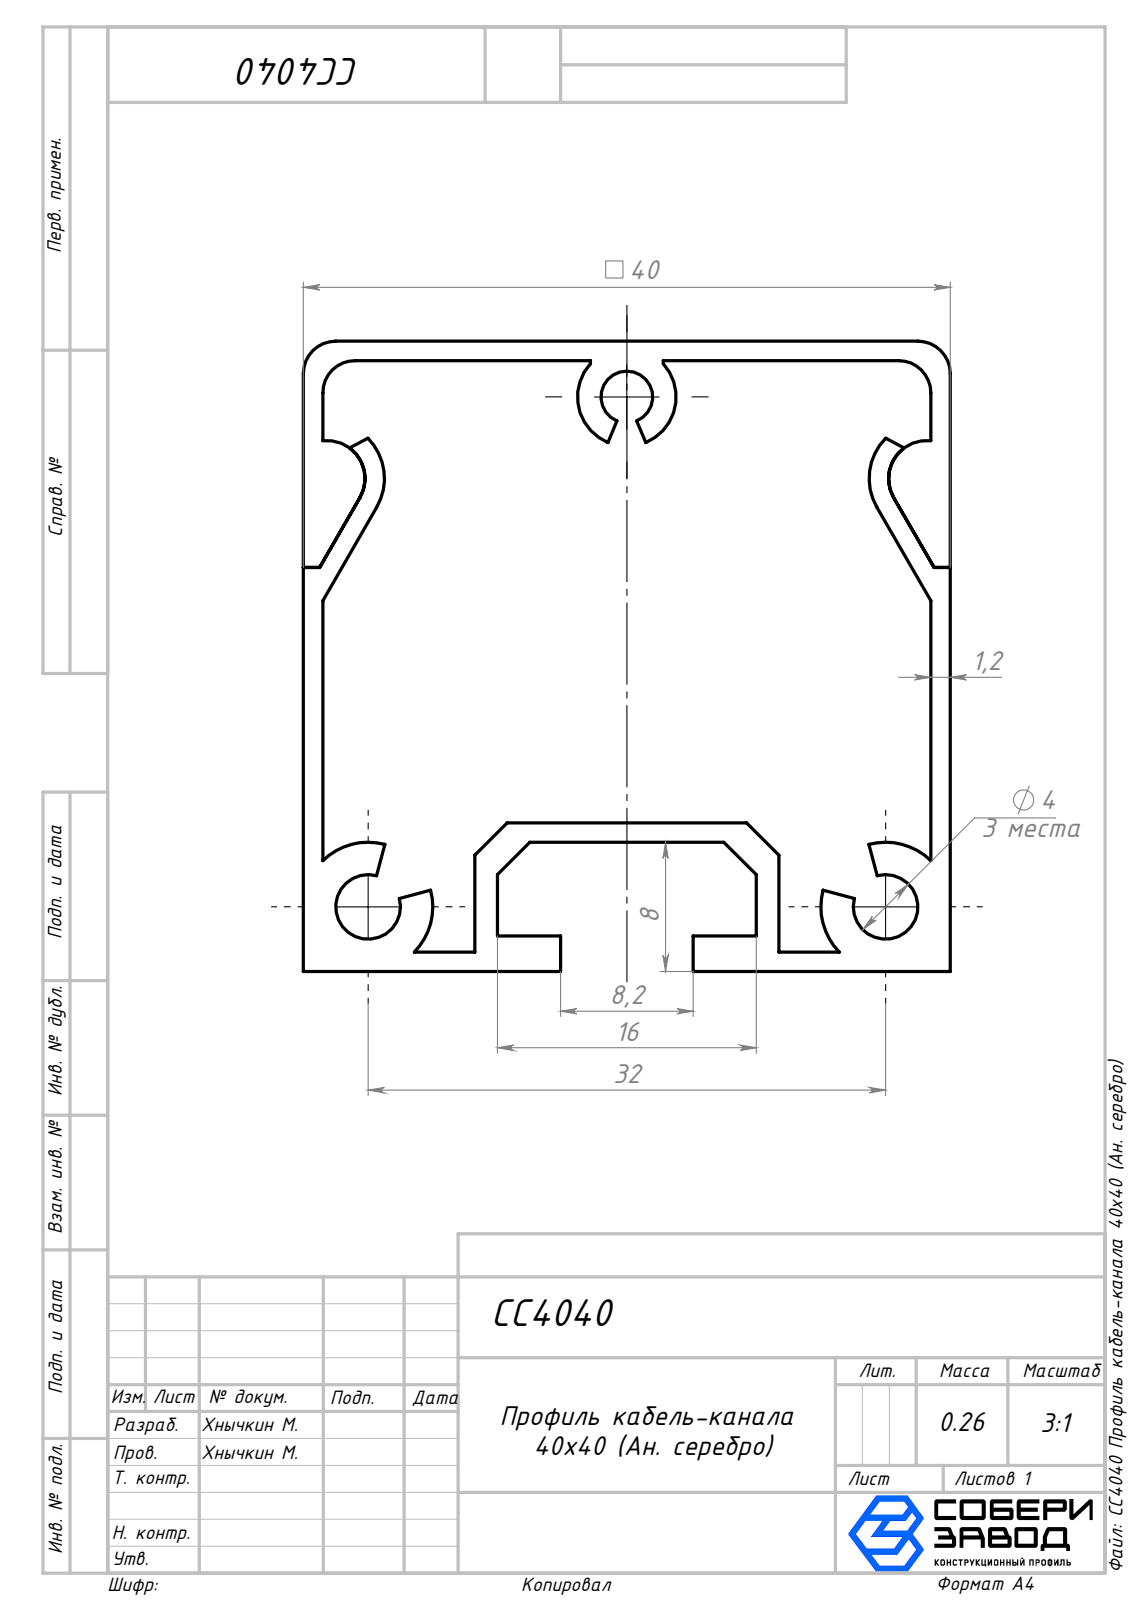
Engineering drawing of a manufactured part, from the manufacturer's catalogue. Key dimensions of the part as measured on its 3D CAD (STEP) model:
Part name (STEP PRODUCT): Алюм. кабель, крышка 40х40_00; Алюм. кабель 40х40_00; CC4040 Профиль кабель-канала 40х40 (Ан. серебро)
STEP written by: SolidWorks 2026 (AUTOMOTIVE_DESIGN)
Units: millimetres
Bodies: 2 solids, 83 faces (53 planar, 30 cylindrical, 0 other)
Overall size (bounding box): 100 × 40 × 39
Volume: 33 182 mm³ · Surface area: 44 135 mm²
Round holes (diameter × count): ⌀4 ×2, ⌀3.2 ×1
Partial cylindrical surfaces — rounded edges, fillets, slot ends (radius × count): R2 ×4, R2.35 ×2, R3.55 ×2, R4 ×2, R3.05 ×1
Main face-to-face distances: 1.2, 38.8, 40, 37.8, 39, 29.8, 8, 37.6, 9.2, 28.6
Hole centre spacings: 35.38, 32
